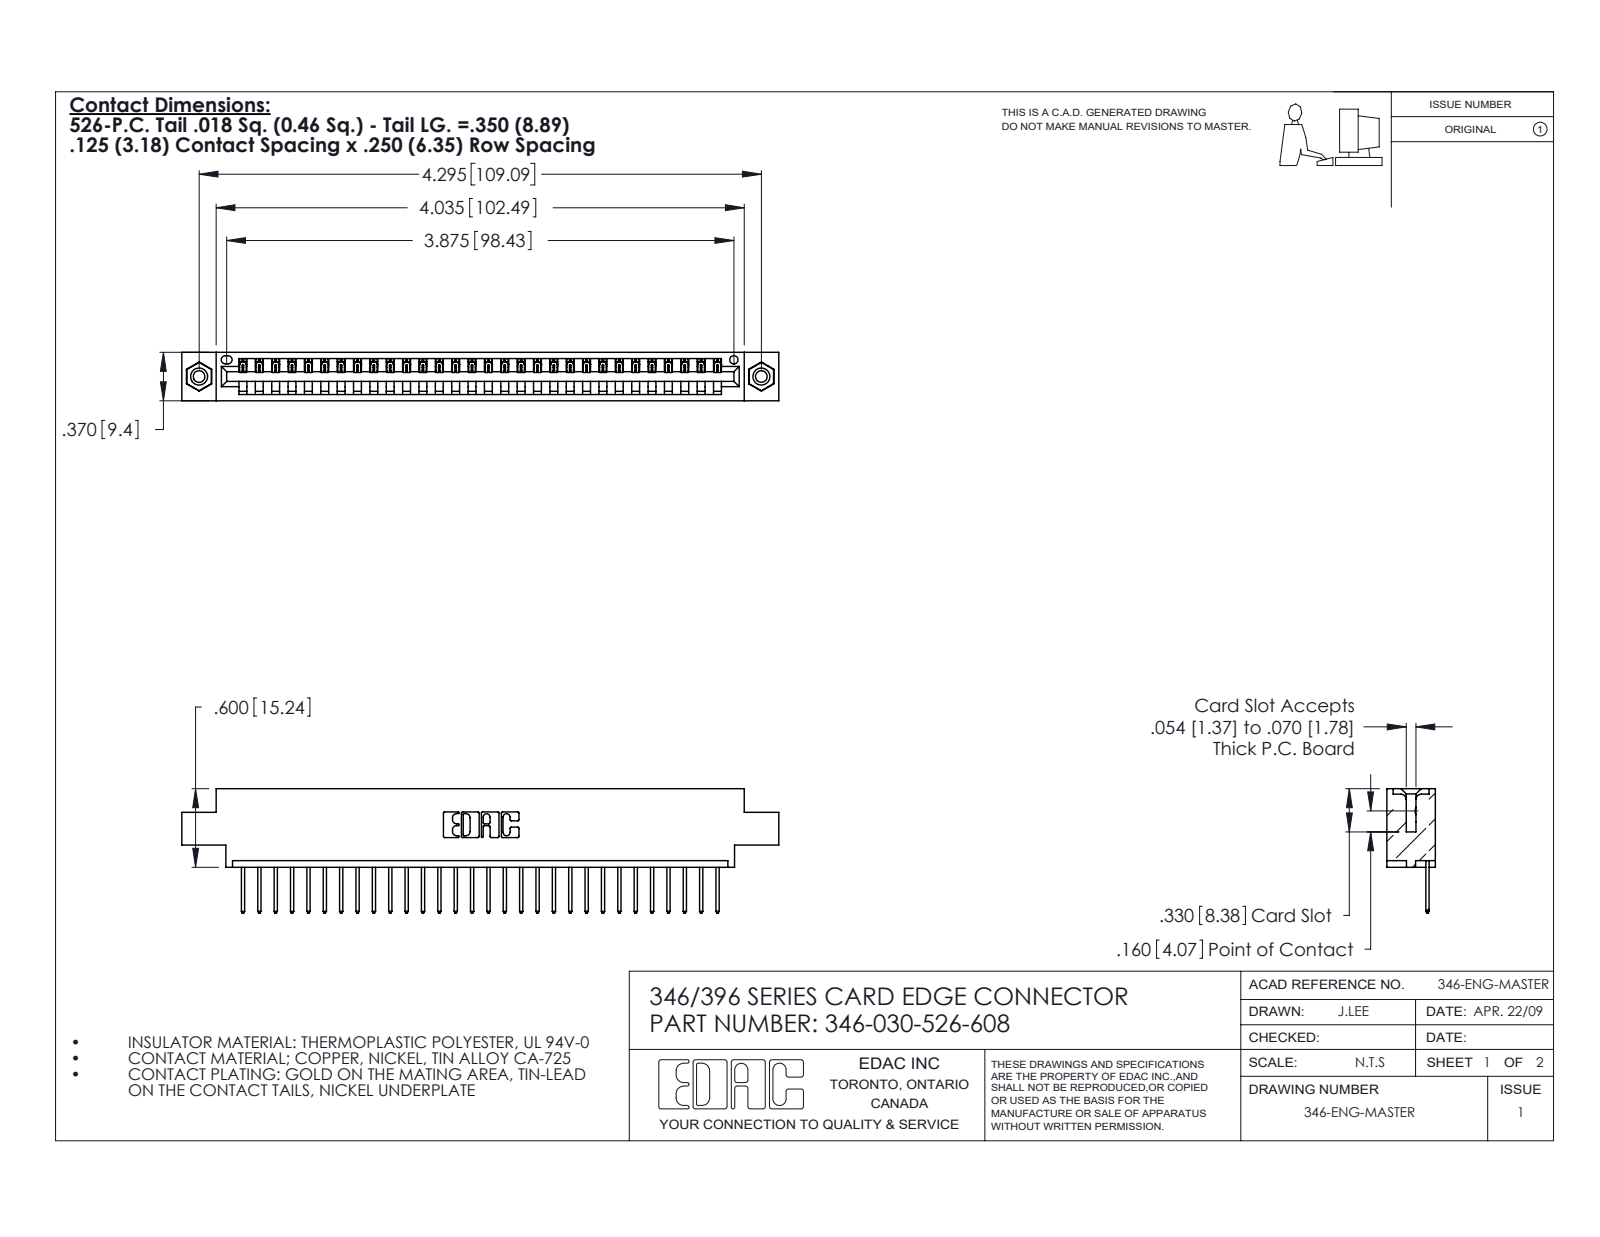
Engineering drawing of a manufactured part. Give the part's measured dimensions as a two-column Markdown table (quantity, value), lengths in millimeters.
| quantity | value |
| --- | --- |
| part name | 345-250-001_345-250-003-102; 346-030-526-608; 346 Part_0.170 Offset - 0.156 Dia-TI; 345-292-001_345-293-126 |
| STEP written by | SolidWorks 2020 (CONFIG_CONTROL_DESIGN) |
| units | millimeters |
| bodies | 33 solids, 1926 faces (1312 planar, 598 cylindrical, 16 other) |
| overall size | 115.8 × 24.1 × 9.4 |
| volume | 10 800 mm³ |
| surface area | 13 550 mm² |
| round holes (diameter × count) | 2.3 × 2, 3.2 × 2, 4 × 2, 1.6 × 1 |
| round bosses / shafts (diameter × count) | 3.9 × 2 |
| partial cylindrical surfaces (radius × count) | 0.2 × 60, 0.3 × 60, 0.3 × 22, 0.2 × 6, 0.8 × 6, 0.7 × 3, 0.8 × 2, 1 × 2 |
| main face-to-face distances | 1.2, 8.2, 9.4, 6.4, 1.8, 7.6, 0.6, 5.6, 3.8, 2.5 |
| hole center spacings | 6.2, 103.8, 109.1 |
